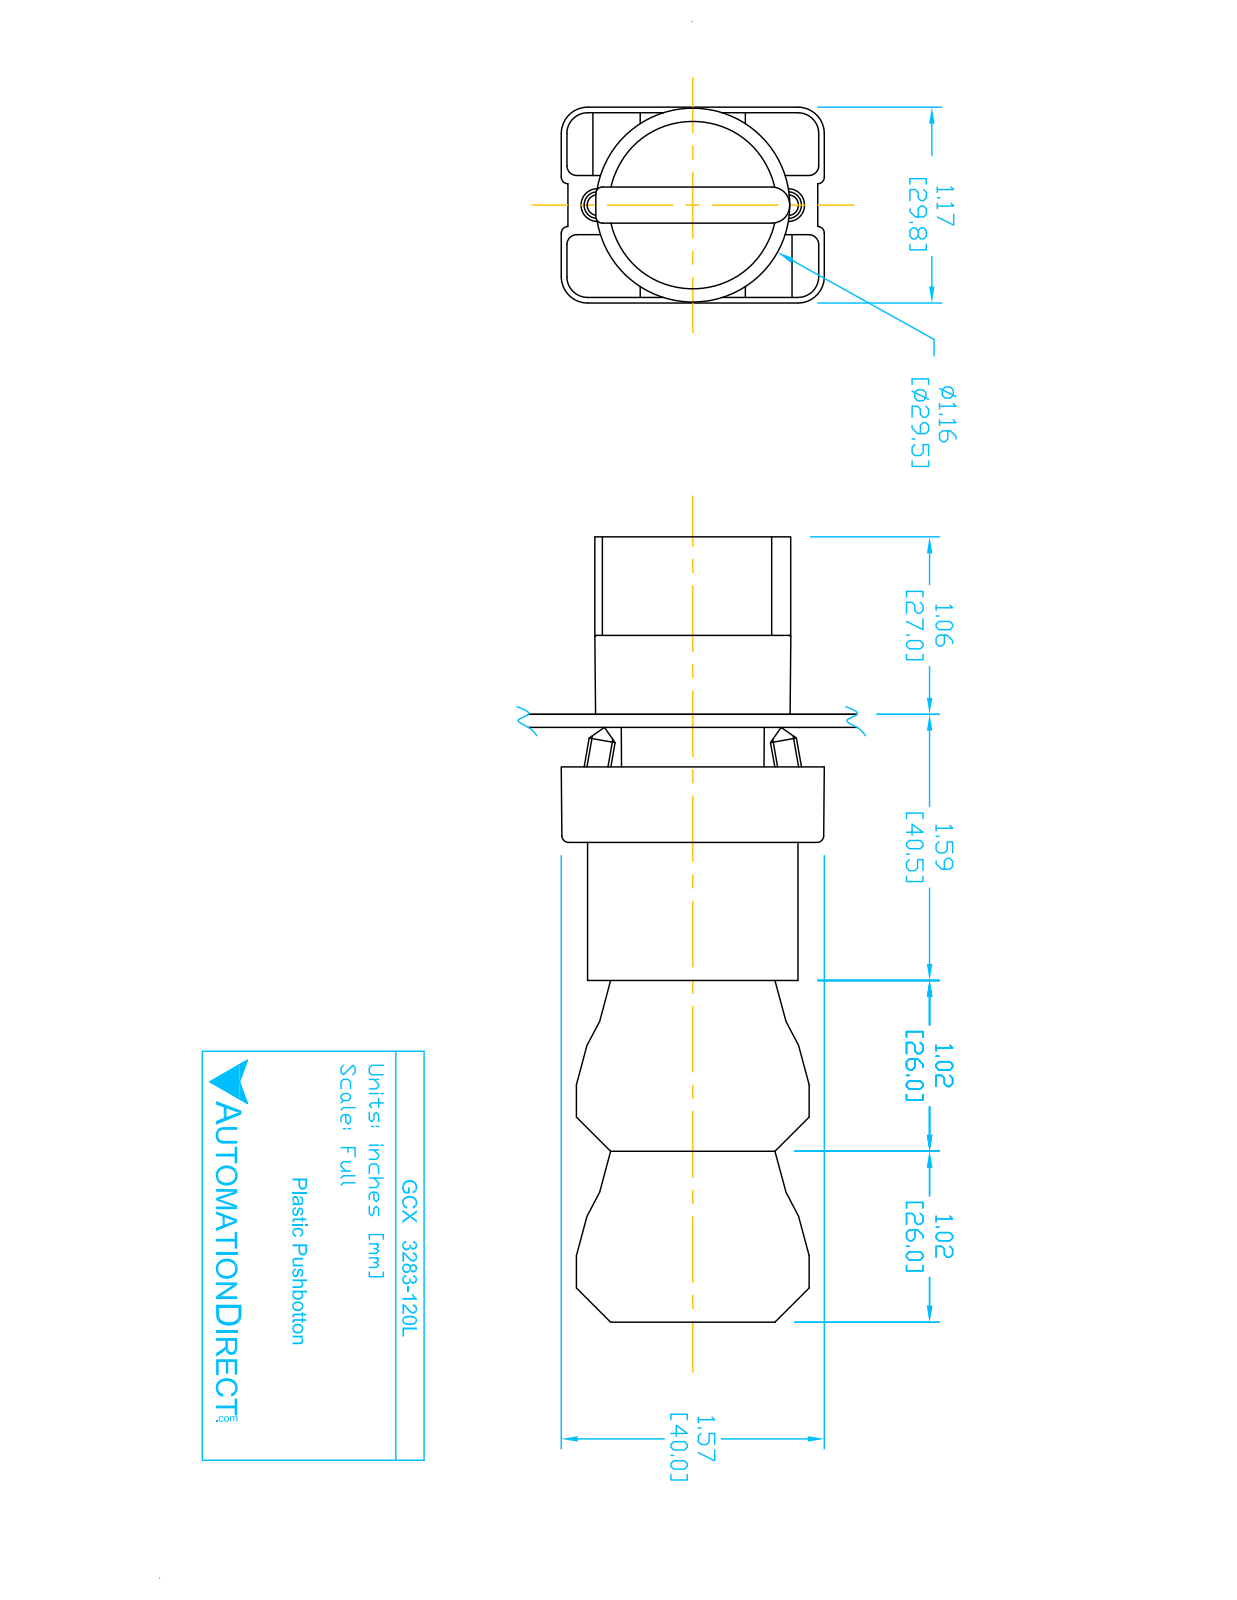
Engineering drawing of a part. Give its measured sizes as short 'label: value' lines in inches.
name: ECX3029-2; ECX1050; GCX3283-120L; ecx1040 (+2 more)
written by: SolidWorks 2016 (AUTOMOTIVE_DESIGN)
unit: in
bodies: 11 solids, 724 faces (488 planar, 193 cylindrical, 43 other)
size: 4.677 × 1.581 × 1.177
volume: 4.751 in³; area: 59.22 in²
holes: 4× ⌀0.079, 2× ⌀0.087, 2× ⌀0.124, 2× ⌀0.13, 1× ⌀0.197, 1× ⌀0.469, 1× ⌀0.878, 1× ⌀0.888, 1× ⌀1.024
bosses: 4× ⌀0.157, 1× ⌀1.175, 1× ⌀1.004, 1× ⌀0.945, 1× ⌀0.856, 1× ⌀0.78, 1× ⌀0.504
rounds: 24× R0.059, 12× R0.041, 12× R0.124, 12× R0.157, 9× R0.039, 2× R0.02, 2× R0.063, 2× R0.079
face distances: 0.579, 0.593, 1.024, 1.171, 0.014, 0.827, 1.85, 3.043, 2.02, 1.193
hole spacings: 0.236, 1.003, 0.974, 0.472, 0.539, 0.544, 1.083, 0.484
